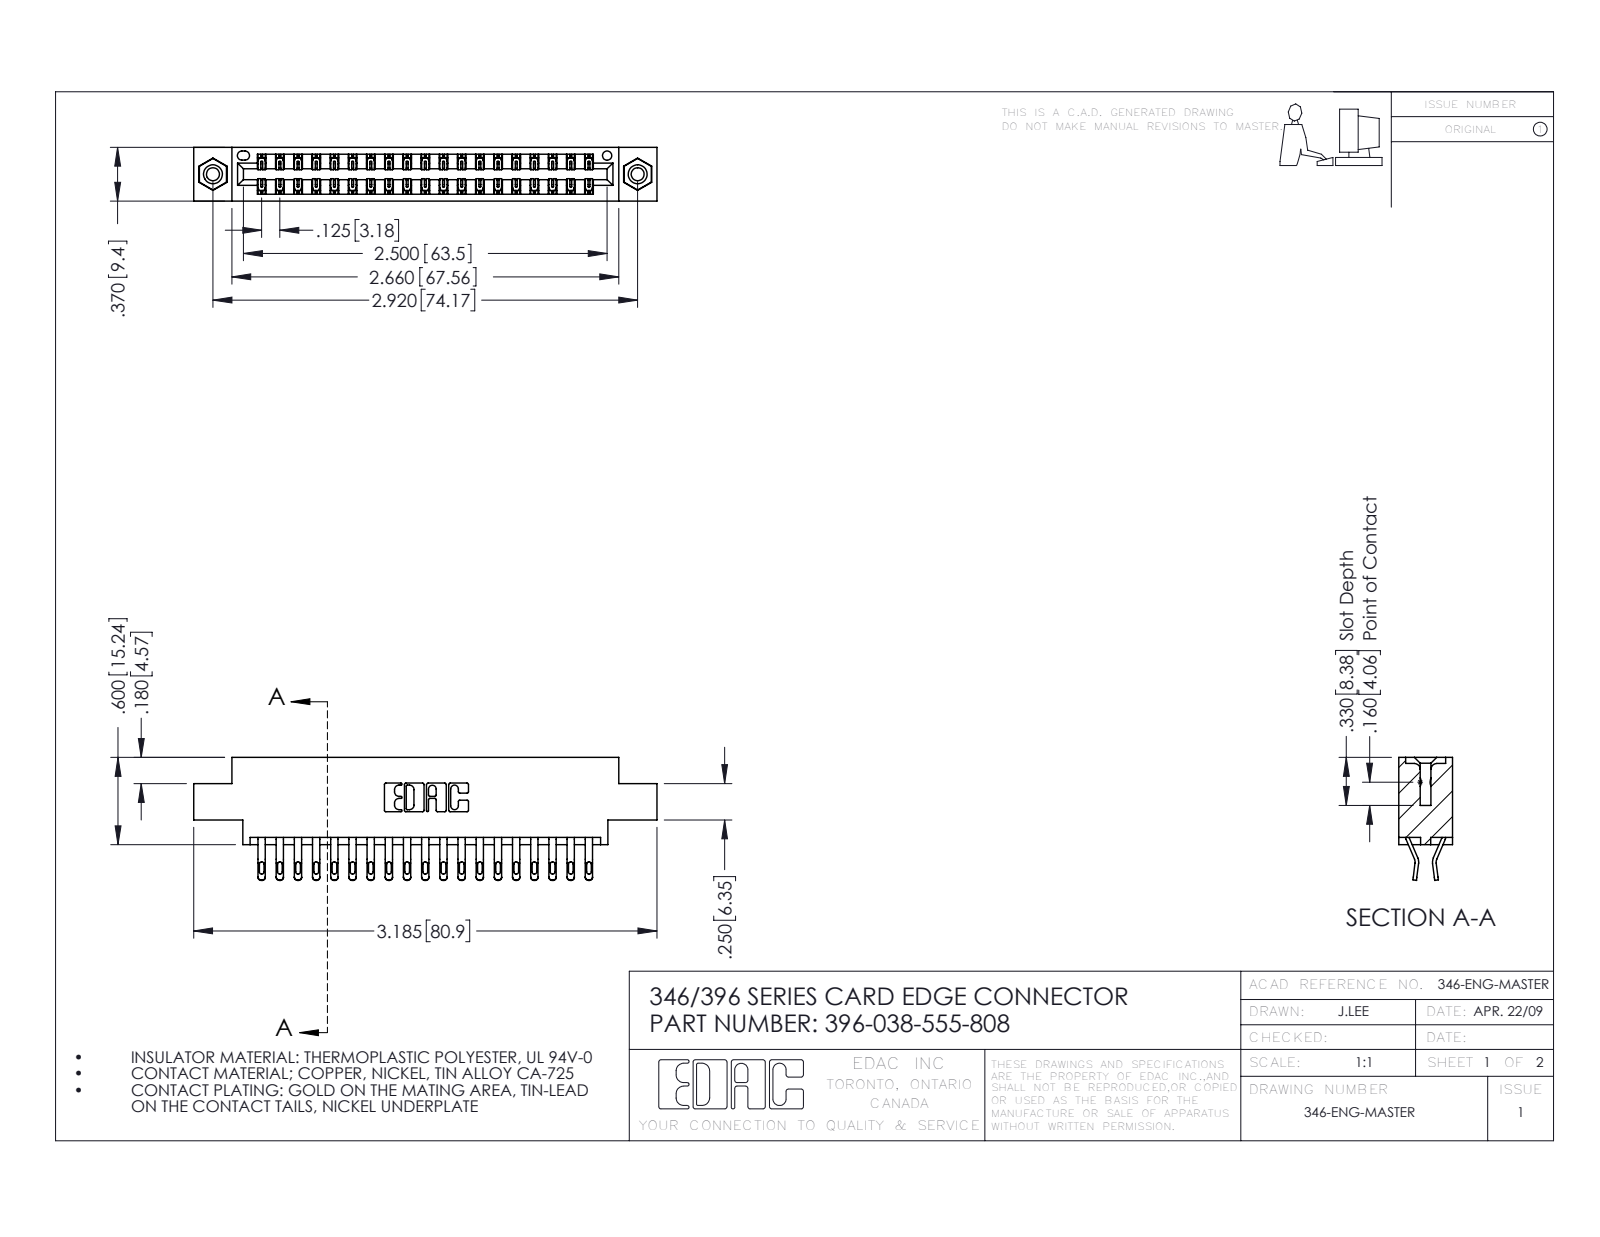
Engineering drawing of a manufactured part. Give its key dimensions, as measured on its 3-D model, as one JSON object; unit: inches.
{"part_name": "396-038-555-808; 346 Part_0.170 Offset - 0.156 Dia-TI; 345-250-001_345-250-003-102; 345-292-001_555 Tail", "step_written_by": "SolidWorks 2016 (CONFIG_CONTROL_DESIGN)", "units": "inches", "bodies": {"solids": 41, "faces": 2390, "planar": 1366, "cylindrical": 1008, "other": 16}, "overall_size": [3.185, 0.845, 0.37], "volume_in3": 0.467, "surface_area_in2": 16.68, "round_holes": [[0.089, 2], [0.125, 2], [0.156, 2], [0.064, 1]], "round_bosses_or_shafts": [[0.155, 2]], "partial_cylinders_radius": [[0.016, 76], [0.02, 76], [0.006, 57], [0.01, 22], [0.007, 6], [0.031, 6], [0.026, 3], [0.01, 2]], "face_to_face_distances": [0.048, 0.322, 0.37, 0.25, 0.025, 0.072, 0.298, 0.275, 0.222, 0.148], "hole_center_spacings": [0.246, 2.713, 2.92]}
